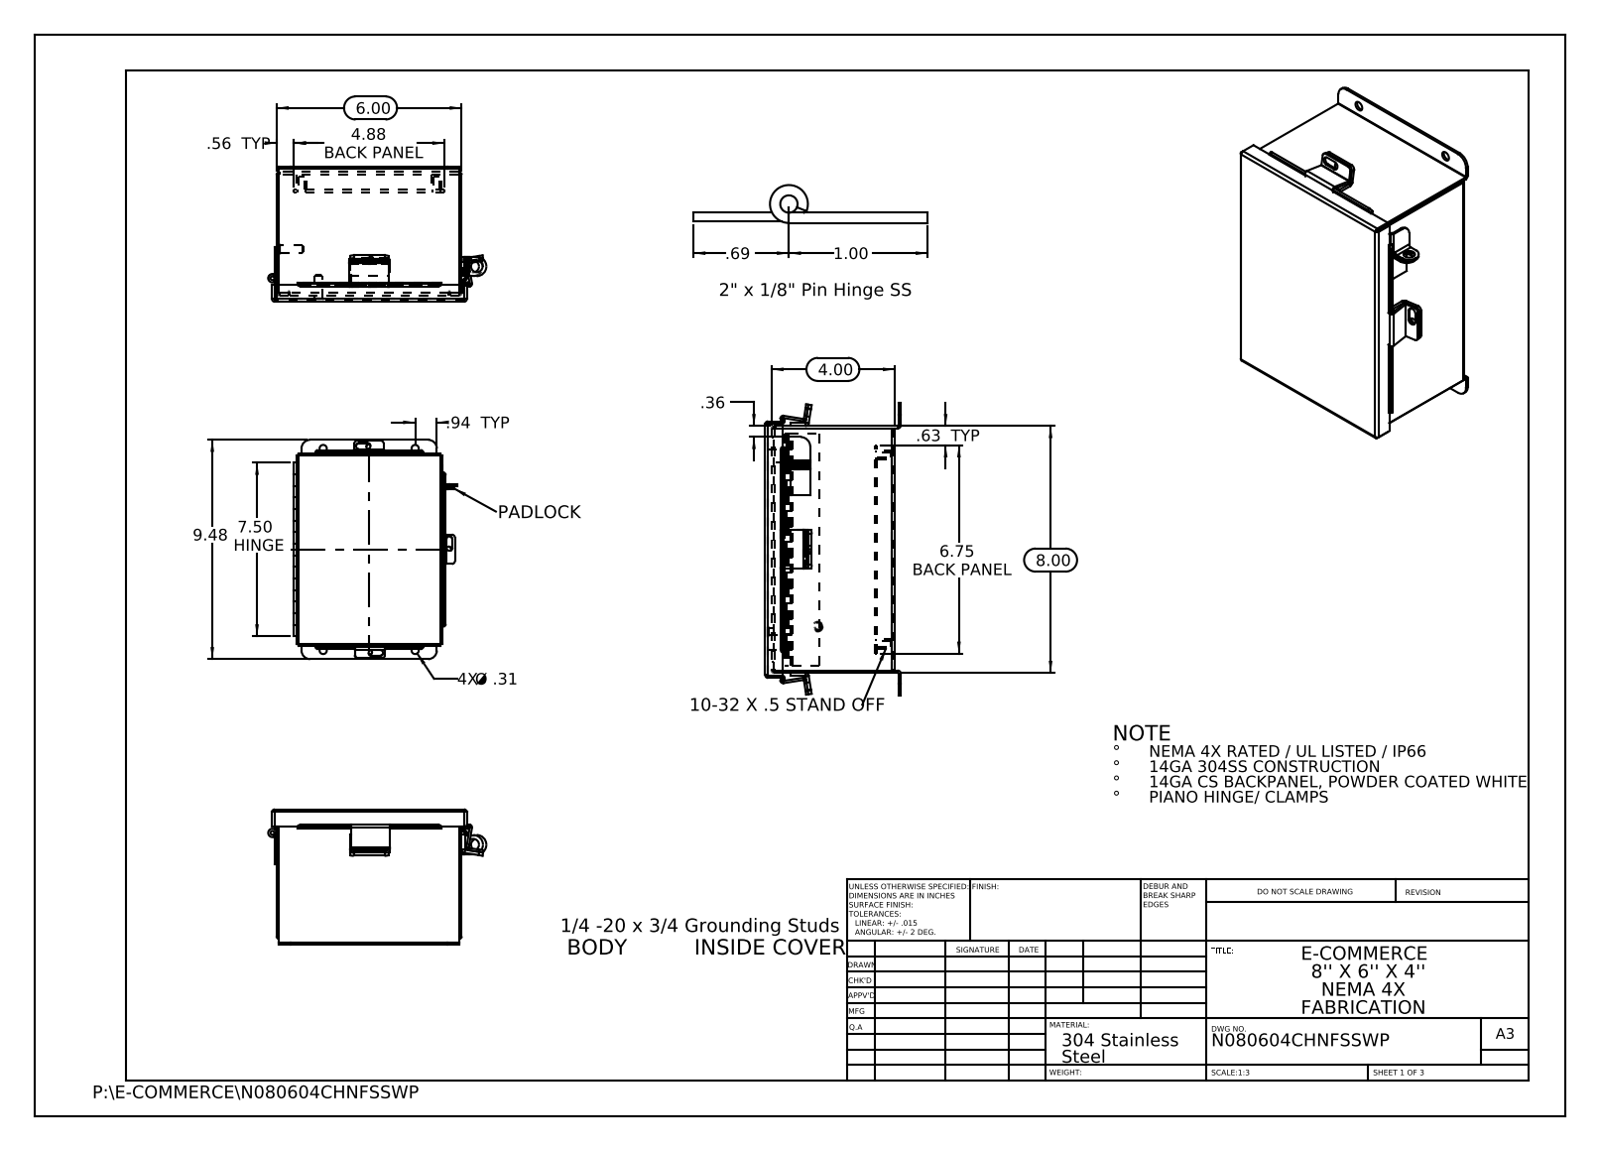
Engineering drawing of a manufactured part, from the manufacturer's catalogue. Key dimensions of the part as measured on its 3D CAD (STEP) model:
Part name (STEP PRODUCT): N080604CHNFSSWP JIC Top; N080604CHNFSSWP JIC Cover Clamp; N080604CHNFSSWP JIC Clamp Bracket; N080604CHNFSSWP JIC Backpanel (+8 more)
STEP written by: SolidWorks 2013 (CONFIG_CONTROL_DESIGN)
Units: inches
Bodies: 21 solids, 584 faces (363 planar, 201 cylindrical, 20 other)
Overall size (bounding box): 9.476 × 7.072 × 4.39
Volume: 22.64 in³ · Surface area: 624.9 in²
Round holes (diameter × count): ⌀0.25 ×7, ⌀0.187 ×4, ⌀0.312 ×4, ⌀0.125 ×1, ⌀0.125 ×1, ⌀0.373 ×1, ⌀0.375 ×1
Round bosses / shafts (diameter × count): ⌀0.313 ×4, ⌀0.315 ×2, ⌀0.236 ×2, ⌀0.273 ×1, ⌀0.25 ×1
Partial cylindrical surfaces — rounded edges, fillets, slot ends (radius × count): R0.013 ×13, R0.009 ×12, R0.088 ×12, R0.125 ×10, R0.083 ×6, R0.1 ×6, R0.133 ×6, R0.375 ×4
Main face-to-face distances: 0.075, 4.128, 5.925, 7.925, 4.053, 4.203, 0.074, 3.479, 0.575, 0.5
Hole centre spacings: 1.315, 4.373, 7.429, 8.519, 3.976, 4.375, 6.126, 7.528
